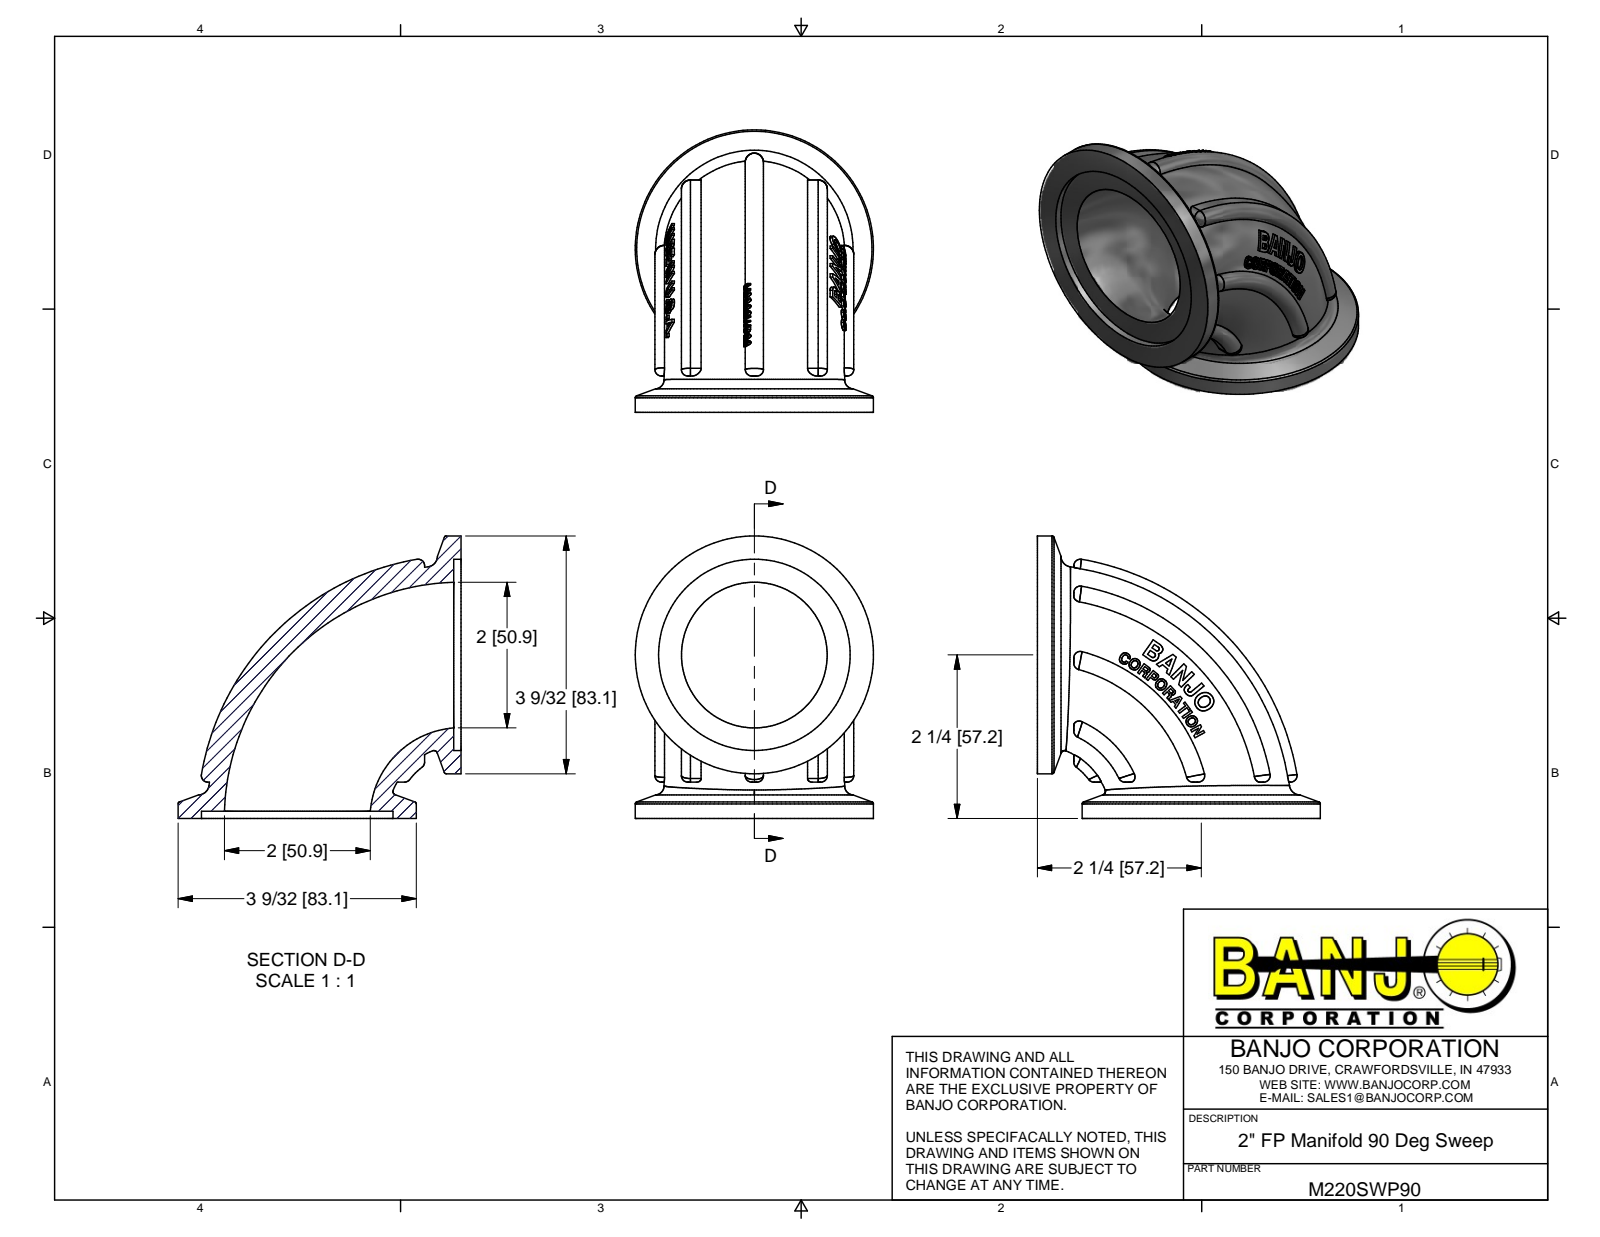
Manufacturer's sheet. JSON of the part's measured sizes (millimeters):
{"part_name": "MxxxSWP90", "step_written_by": "Autodesk Inventor 2014 (AUTOMOTIVE_DESIGN)", "units": "millimeters", "bodies": {"solids": 1, "faces": 578, "planar": 264, "cylindrical": 16, "other": 298}, "overall_size": [98.68, 98.68, 83.06], "volume_mm3": 132719, "surface_area_mm2": 45525, "round_holes": [[66.8, 2]], "round_bosses_or_shafts": [[83.06, 2]], "partial_cylinders_radius": [[2.29, 4], [31.7, 1], [82.6, 1]], "face_to_face_distances": [2.54, 12.7, 10.16, 1.05, 1.31, 1.04, 5.08, 0.78, 0.88, 3.86]}
